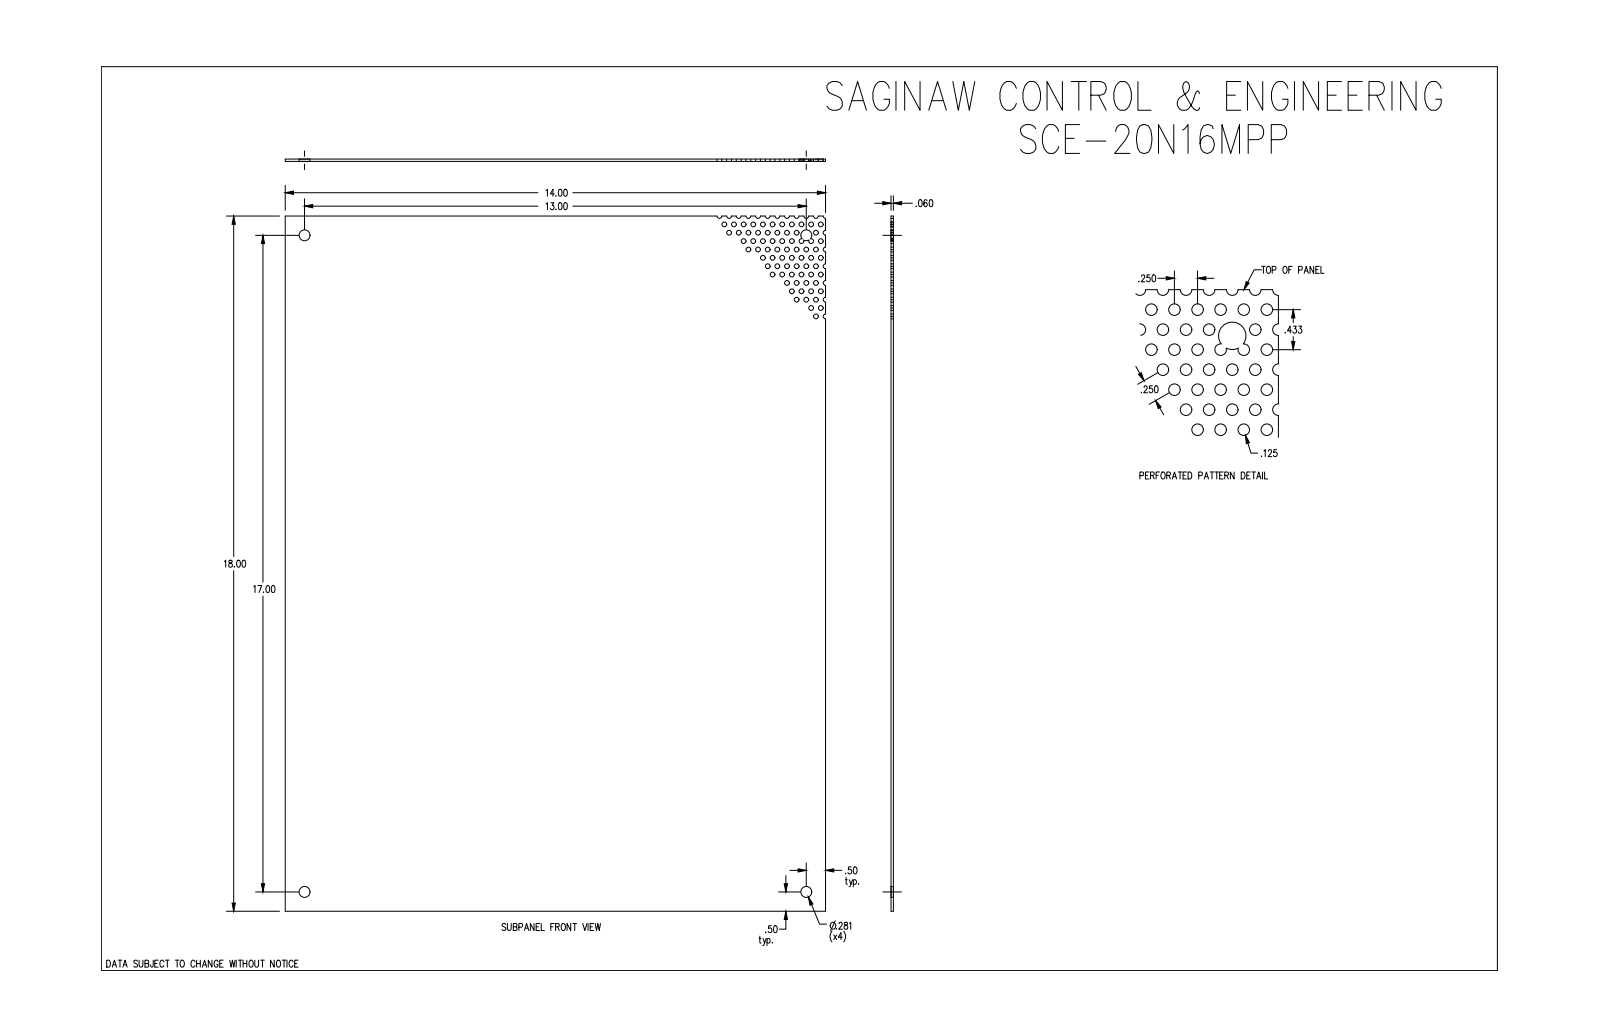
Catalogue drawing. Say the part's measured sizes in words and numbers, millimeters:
The part is named "SCE-20N16MPP". Its 3-D file was written by "SolidWorks 2019 (CONFIG_CONTROL_DESIGN)". It is 1 solid with 116 faces: 23 planar, 93 cylindrical and 0 other. Overall it measures 457.2 by 355.6 by 1.5 millimeters. Its volume is 246 600 cubic millimeters and its surface area 327 300 square millimeters. Round holes: 66 of diameter 3.2, 4 of diameter 3.2, 4 of diameter 7.1. Partial cylindrical surfaces (rounded edges, fillets, slot ends): 15 of radius 1.6, 3 of radius 1.6. The main face-to-face distances are 1.5, 355.6, 457.2. The hole center spacings are 6.4, 16.8, 12.7, 11, 11, 19.1, 22.9, 33.6.
